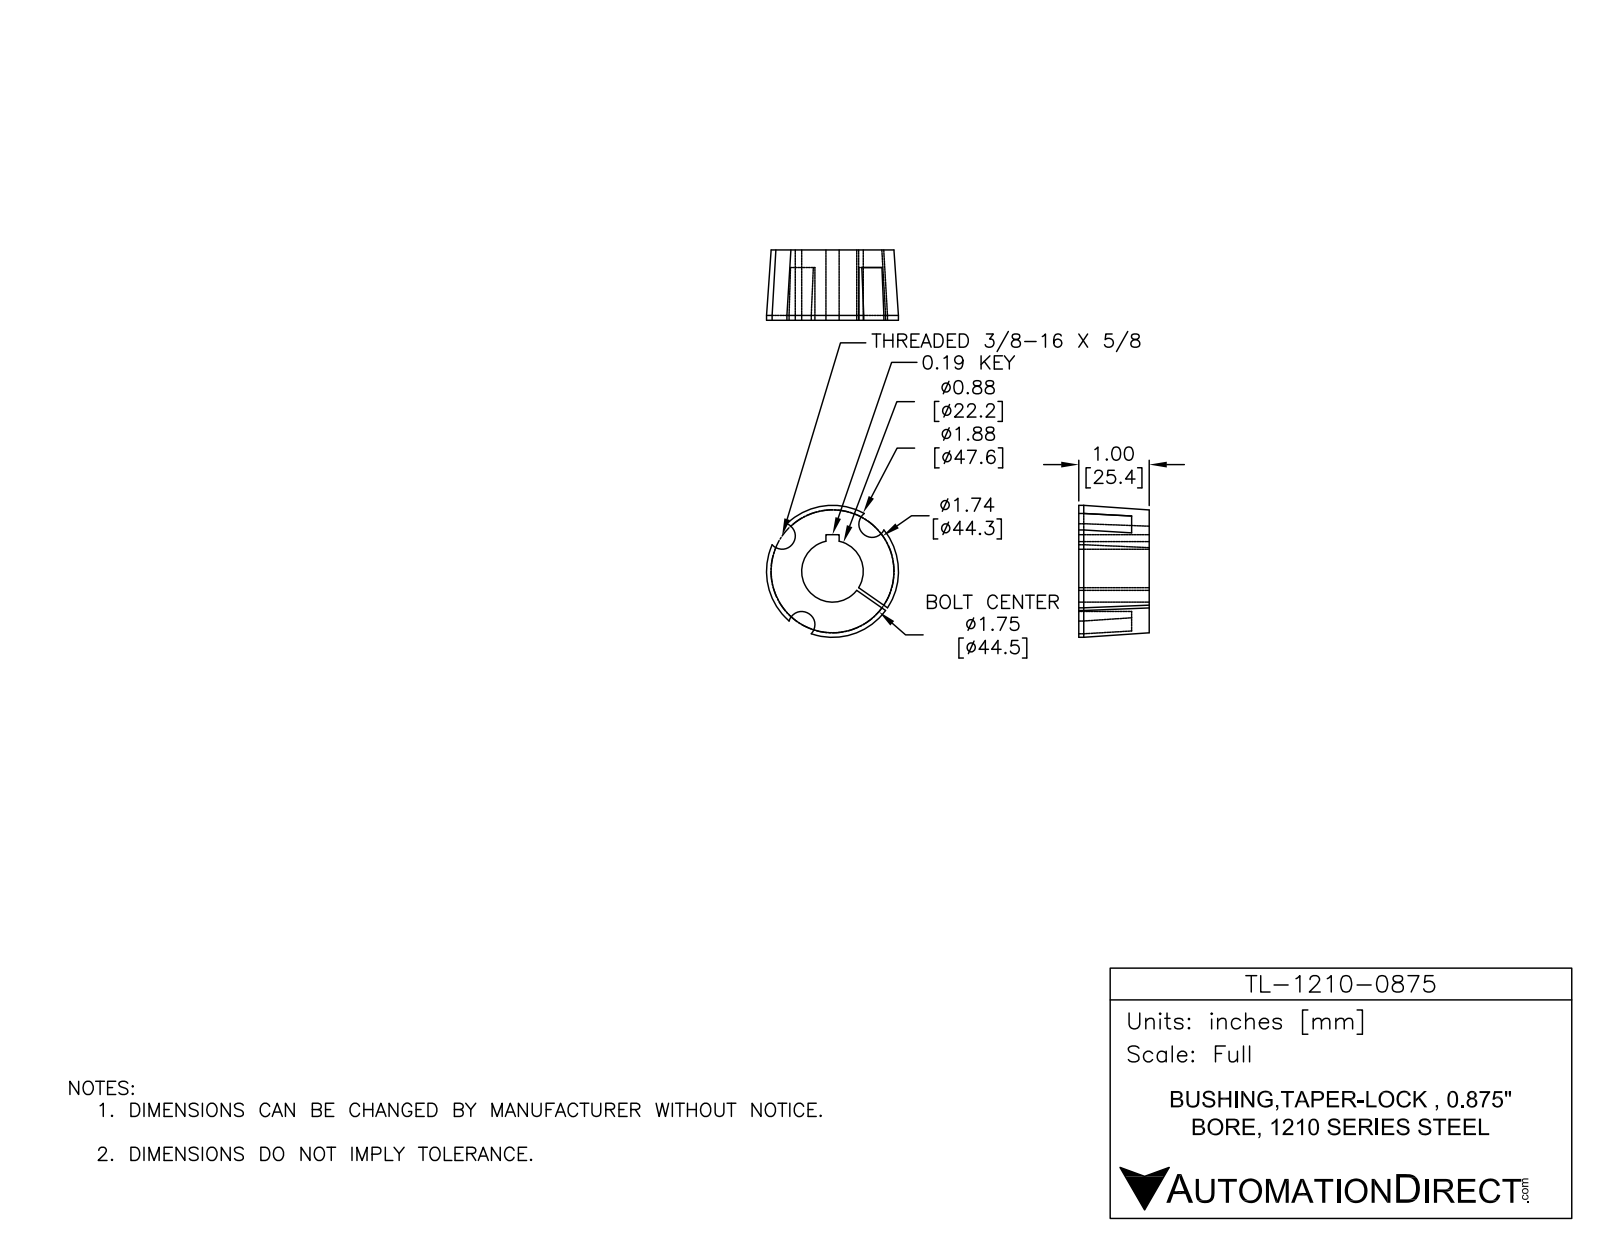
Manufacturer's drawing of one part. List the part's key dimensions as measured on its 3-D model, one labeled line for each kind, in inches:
Part name (STEP PRODUCT): TL-1210-0875
STEP written by: SolidWorks 2014 (AUTOMOTIVE_DESIGN)
Units: inches
Bodies: 1 solid, 25 faces (9 planar, 13 cylindrical, 3 other)
Overall size (bounding box): 1.875 × 1.875 × 1
Volume: 1.782 in³ · Surface area: 13.82 in²
Round holes (diameter × count): ⌀0.875 ×1
Round bosses / shafts (diameter × count): ⌀1.875 ×1
Partial cylindrical surfaces — rounded edges, fillets, slot ends (radius × count): R0.188 ×3
Main face-to-face distances: 1, 0.048, 0.25, 0.75, 0.187
